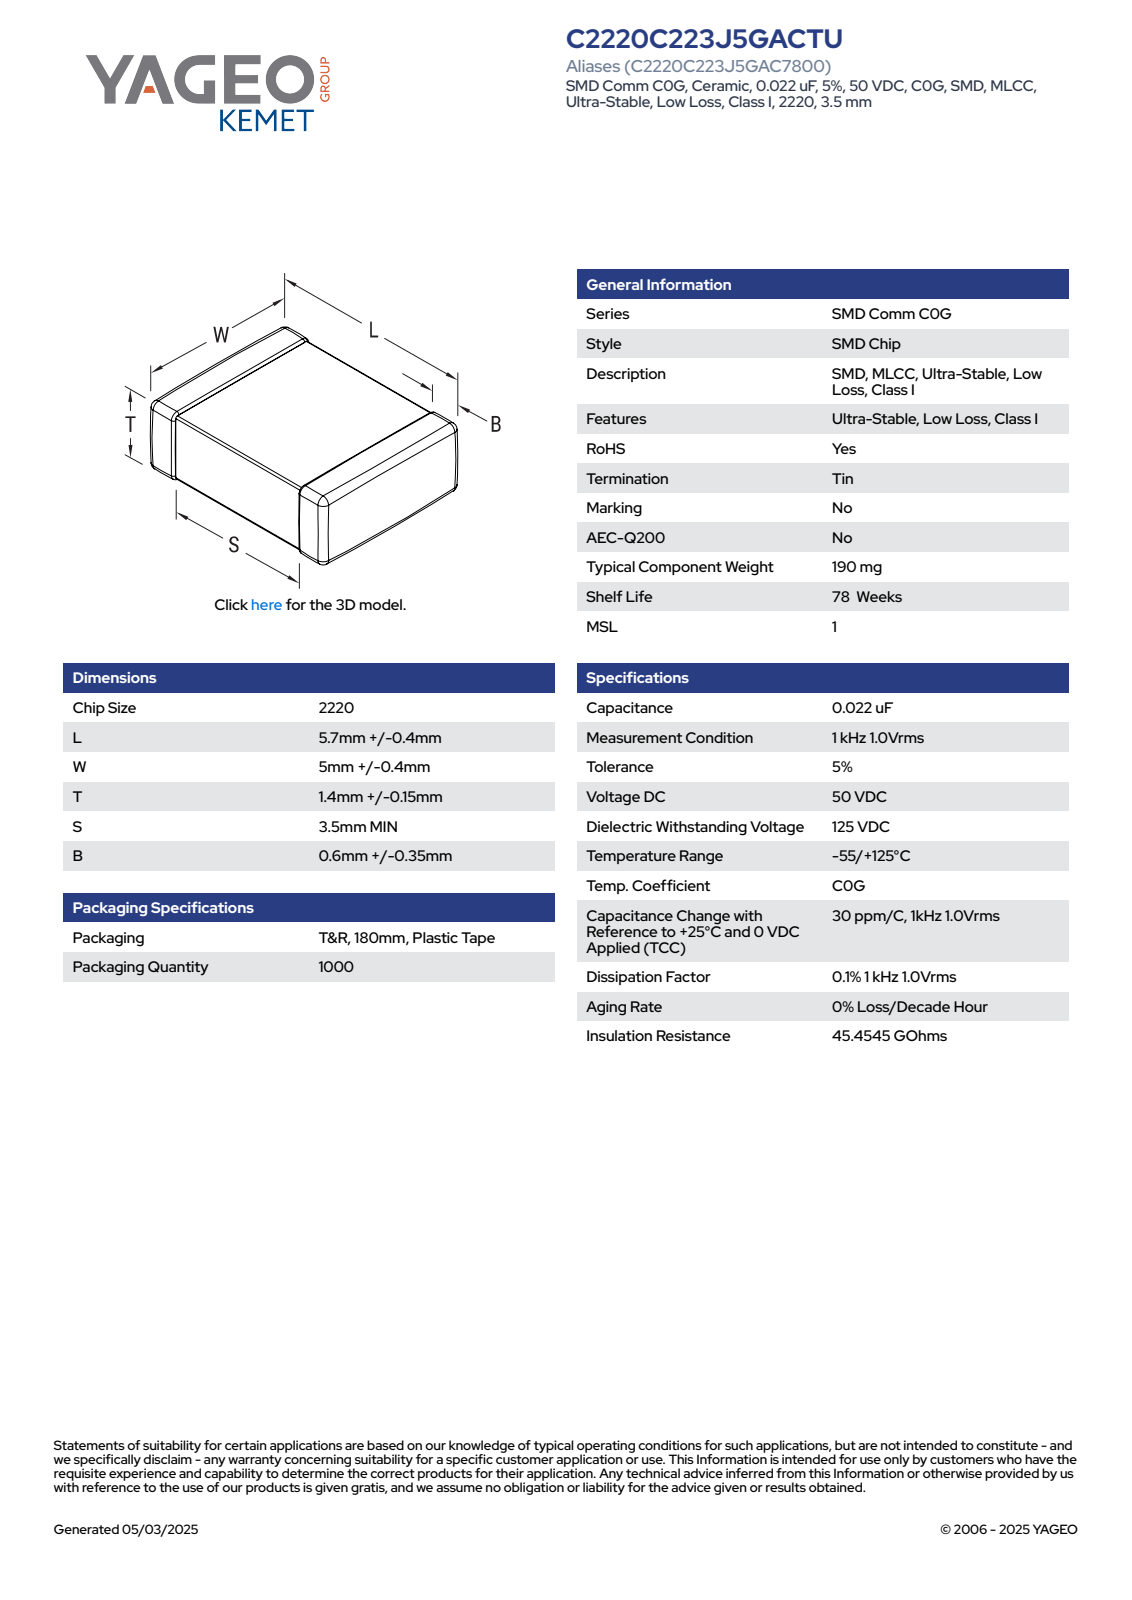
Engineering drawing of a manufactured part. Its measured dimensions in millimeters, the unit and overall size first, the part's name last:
Units: millimetres
Overall size (bounding box): 6.1 × 5.4 × 1.55
Partial cylindrical surfaces — rounded edges, fillets, slot ends (radius × count): R0.11 ×24
Main face-to-face distances: 1.33, 1.44, 1.55, 6.1, 5.18, 5.29, 5.4, 2.5, 3.6, 3.29
Volume: 45 mm³ · Surface area: 101 mm²
Bodies: 4 solids, 125 faces (71 planar, 38 cylindrical, 16 other)
Part name (STEP PRODUCT): CCS_CCSTD_2220_L6.1W5.4T1.55B0.6
STEP written by: SolidWorks 2021 (AUTOMOTIVE_DESIGN)
